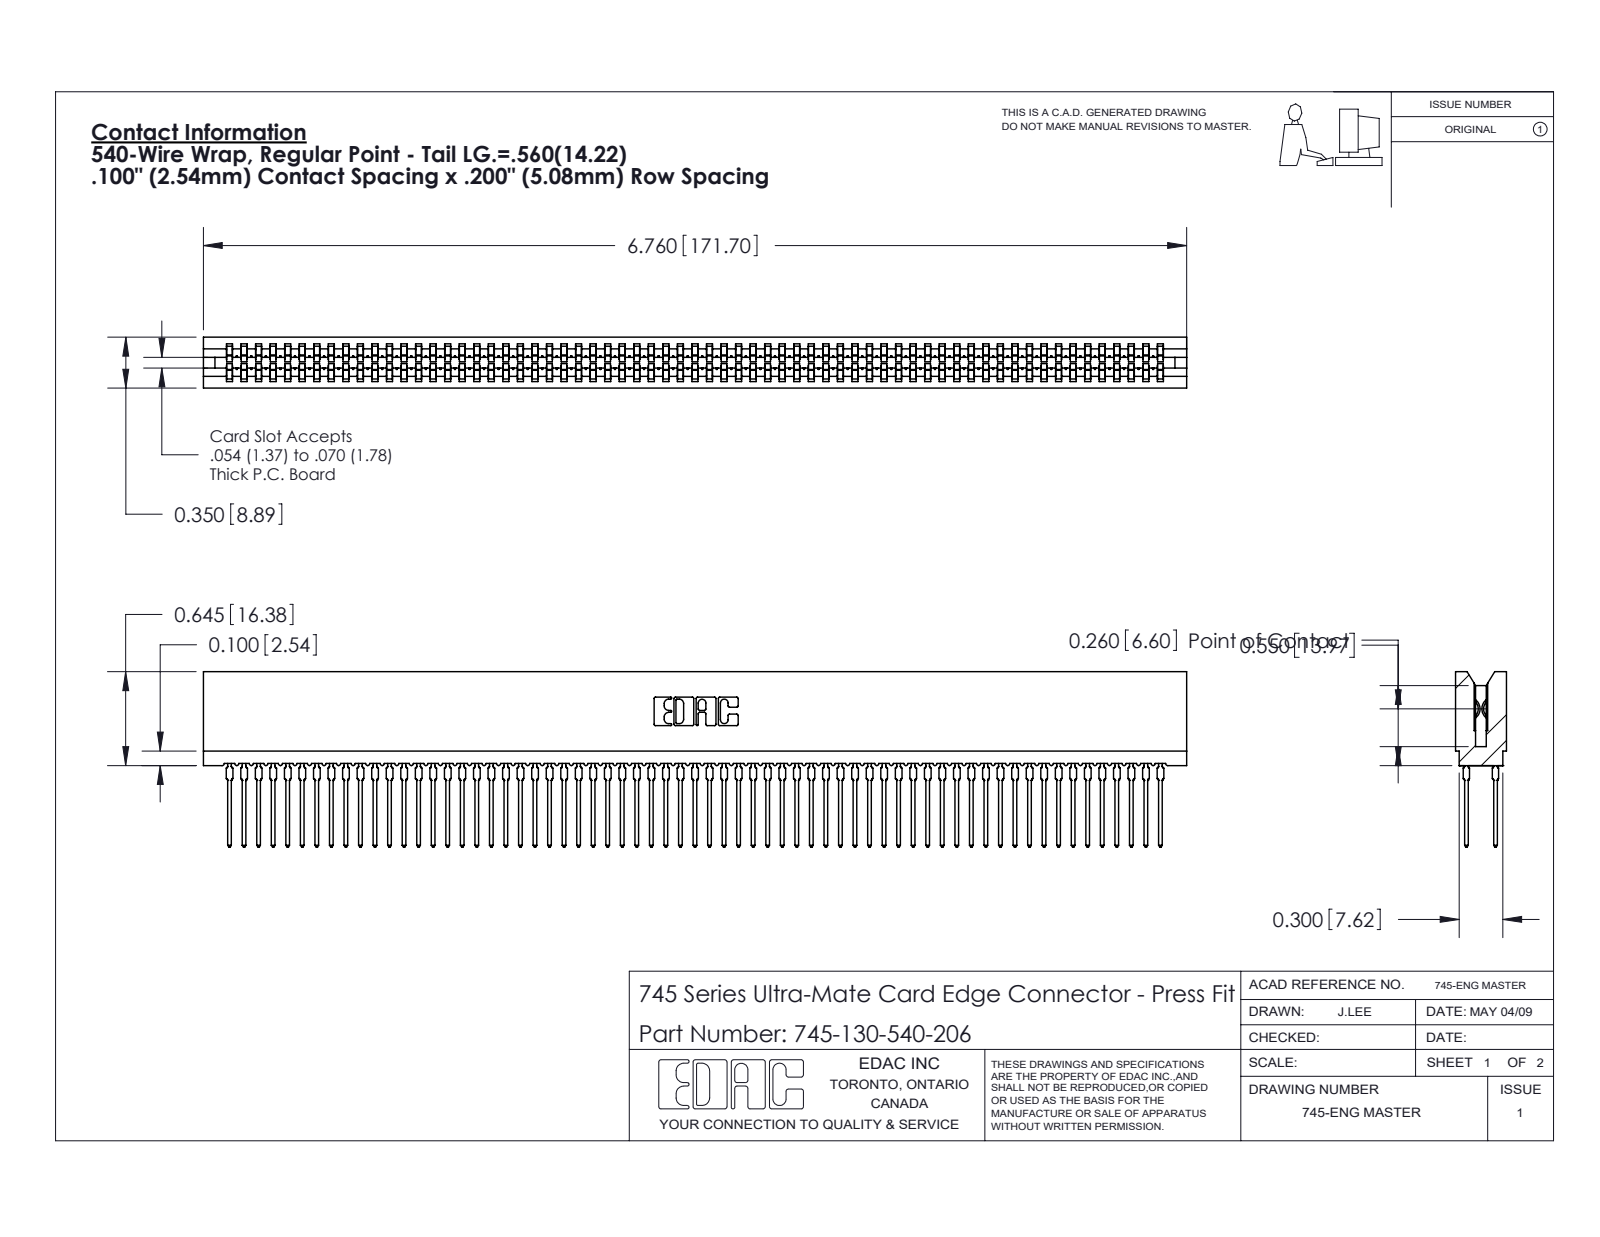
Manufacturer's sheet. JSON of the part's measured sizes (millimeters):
{"part_name": "745-292-001_540; 745 Part_Insulator Option - 06; 745-130-540-206", "step_written_by": "SolidWorks 2020 (CONFIG_CONTROL_DESIGN)", "units": "millimeters", "bodies": {"solids": 131, "faces": 11731, "planar": 6036, "cylindrical": 2315, "other": 3380}, "overall_size": [171.7, 30.6, 8.9], "volume_mm3": 15700, "surface_area_mm2": 33950, "partial_cylinders_radius": [[0.5, 260], [0.4, 130], [0.3, 22], [0.1, 8], [0.3, 8], [0.2, 6], [0.8, 6], [0.7, 3]], "face_to_face_distances": [1.6, 7.3, 8.9, 1.1, 7.7, 0.5, 6.2, 3.5, 5.4, 2.4]}
